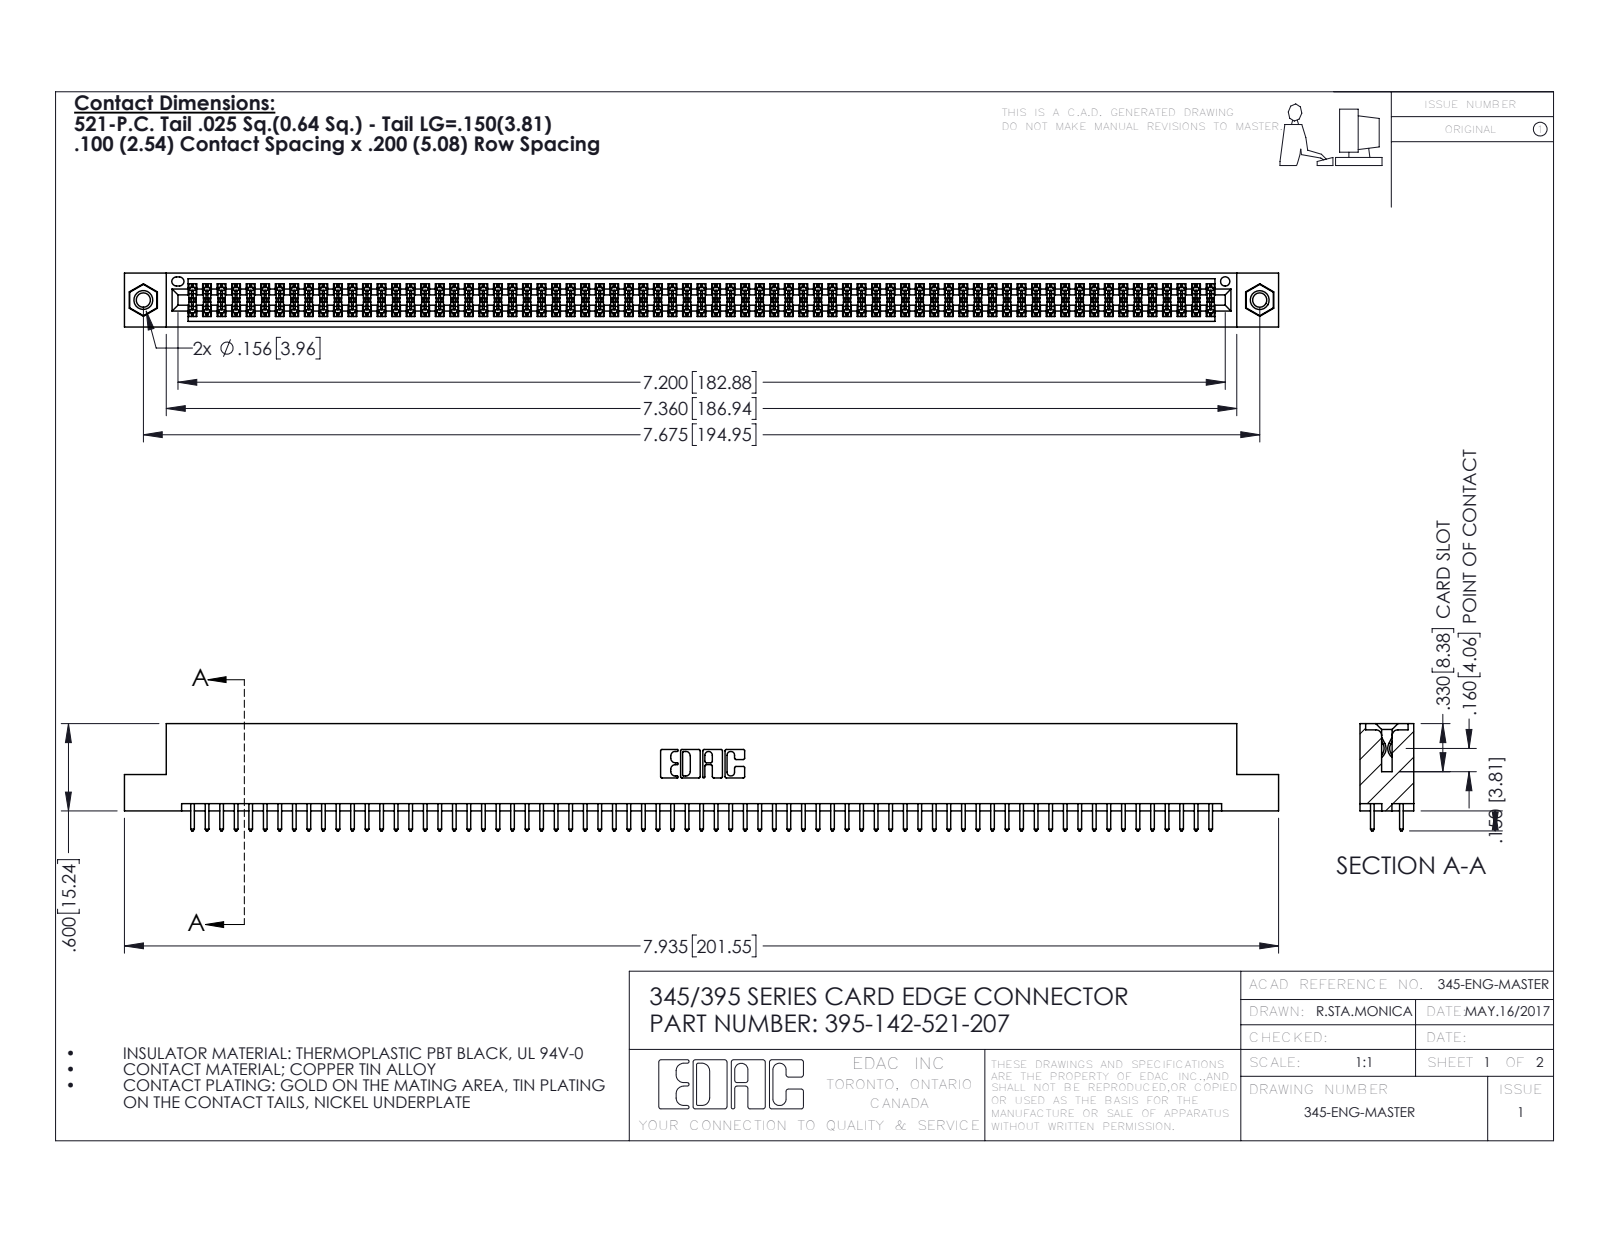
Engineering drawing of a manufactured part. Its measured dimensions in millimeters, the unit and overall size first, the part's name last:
Units: millimetres
Overall size (bounding box): 201.5 × 18.7 × 9.4
Round holes (diameter × count): ⌀2.5 ×2, ⌀3.2 ×2, ⌀4 ×2, ⌀1.6 ×1
Round bosses / shafts (diameter × count): ⌀3.9 ×2
Partial cylindrical surfaces — rounded edges, fillets, slot ends (radius × count): R0.2 ×213, R0.3 ×142, R0.3 ×22, R0.2 ×6, R0.8 ×6, R0.7 ×3, R0.4 ×2, R0.5 ×2
Main face-to-face distances: 1.8, 7.6, 5.1, 2.5, 6.9, 0.6, 9.4, 5.7, 4.4, 3.8
Hole centre spacings: 6.9, 189, 194.9
Volume: 19 780 mm³ · Surface area: 29 450 mm²
Bodies: 145 solids, 7286 faces (4798 planar, 2472 cylindrical, 16 other)
Part name (STEP PRODUCT): 345-250-001_345-250-005-103; 345-292-001_345-293-121; 345 Part_Flush Mounting Lugs - 0.156 Dia-TI; 395-142-521-207
STEP written by: SolidWorks 2016 (CONFIG_CONTROL_DESIGN)
